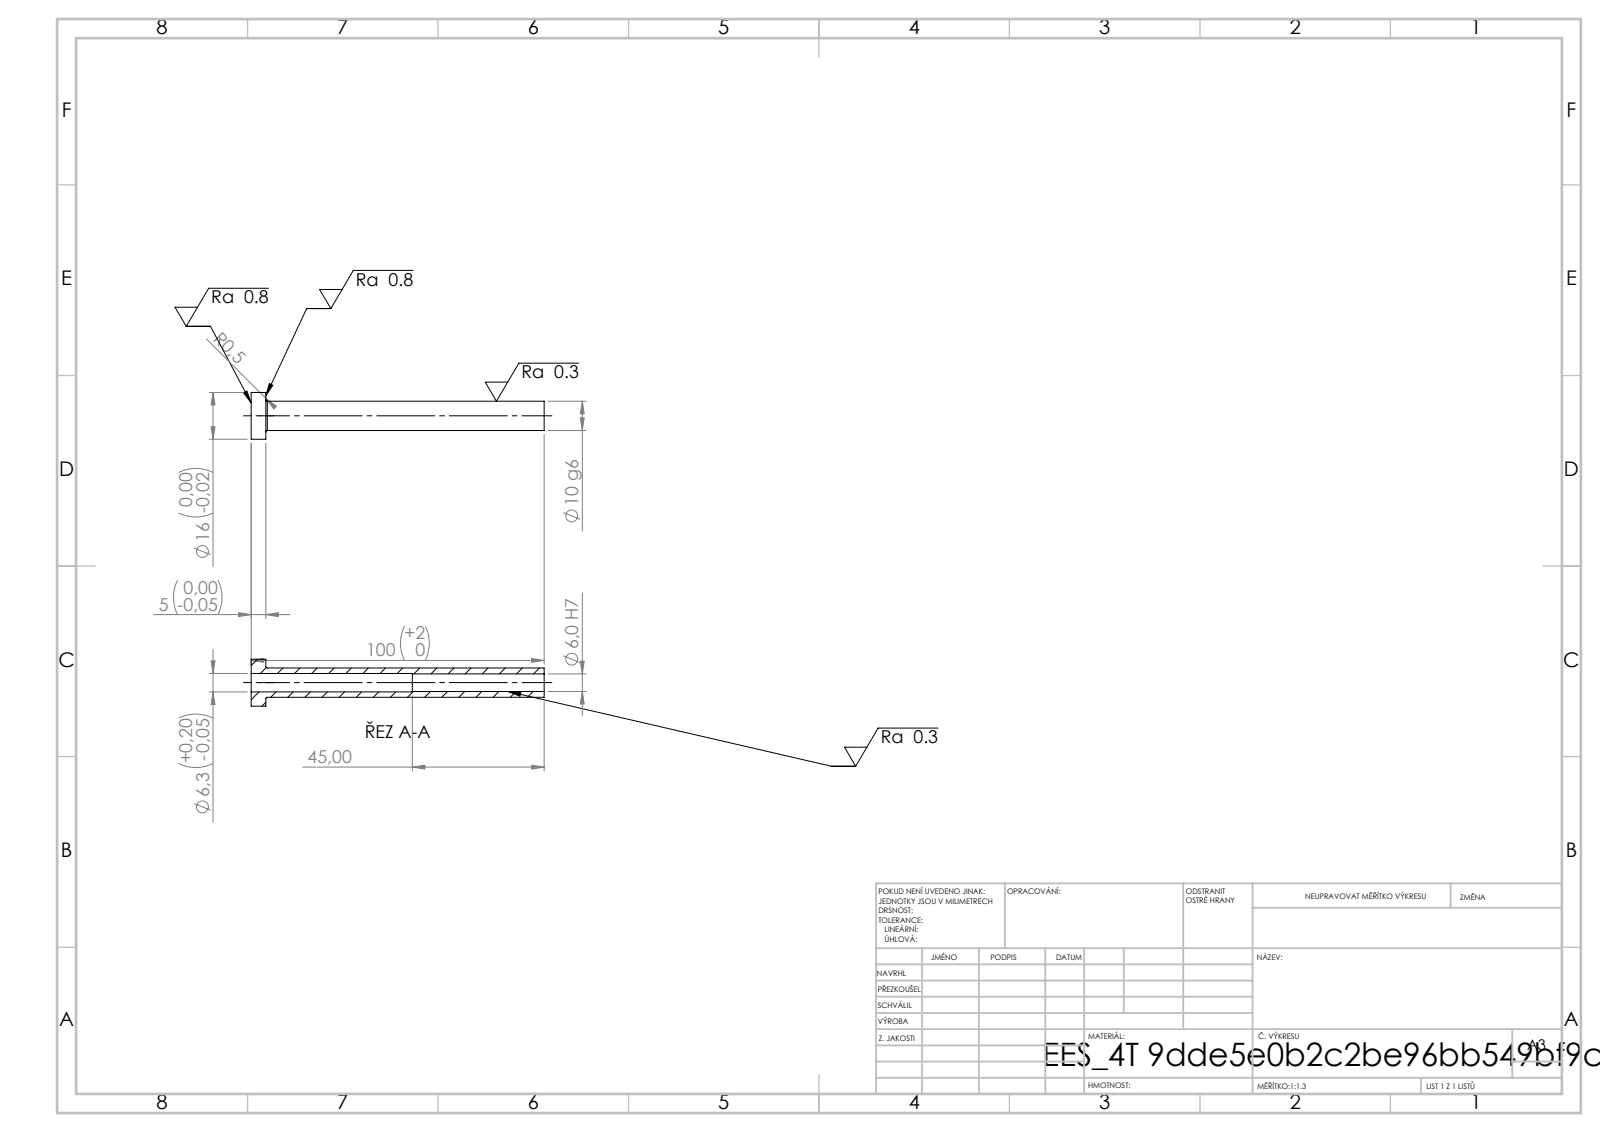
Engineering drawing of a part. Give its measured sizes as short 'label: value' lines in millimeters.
written by: SolidWorks 2019 (CONFIG_CONTROL_DESIGN)
unit: mm
bodies: 1 solid, 14 faces (4 planar, 8 cylindrical, 2 other)
size: 100 × 16 × 16
volume: 5 481 mm³; area: 5 512 mm²
holes: 1× ⌀6, 1× ⌀6.3
bosses: 1× ⌀16, 1× ⌀10
face distances: 5, 100, 95, 55, 50, 45
